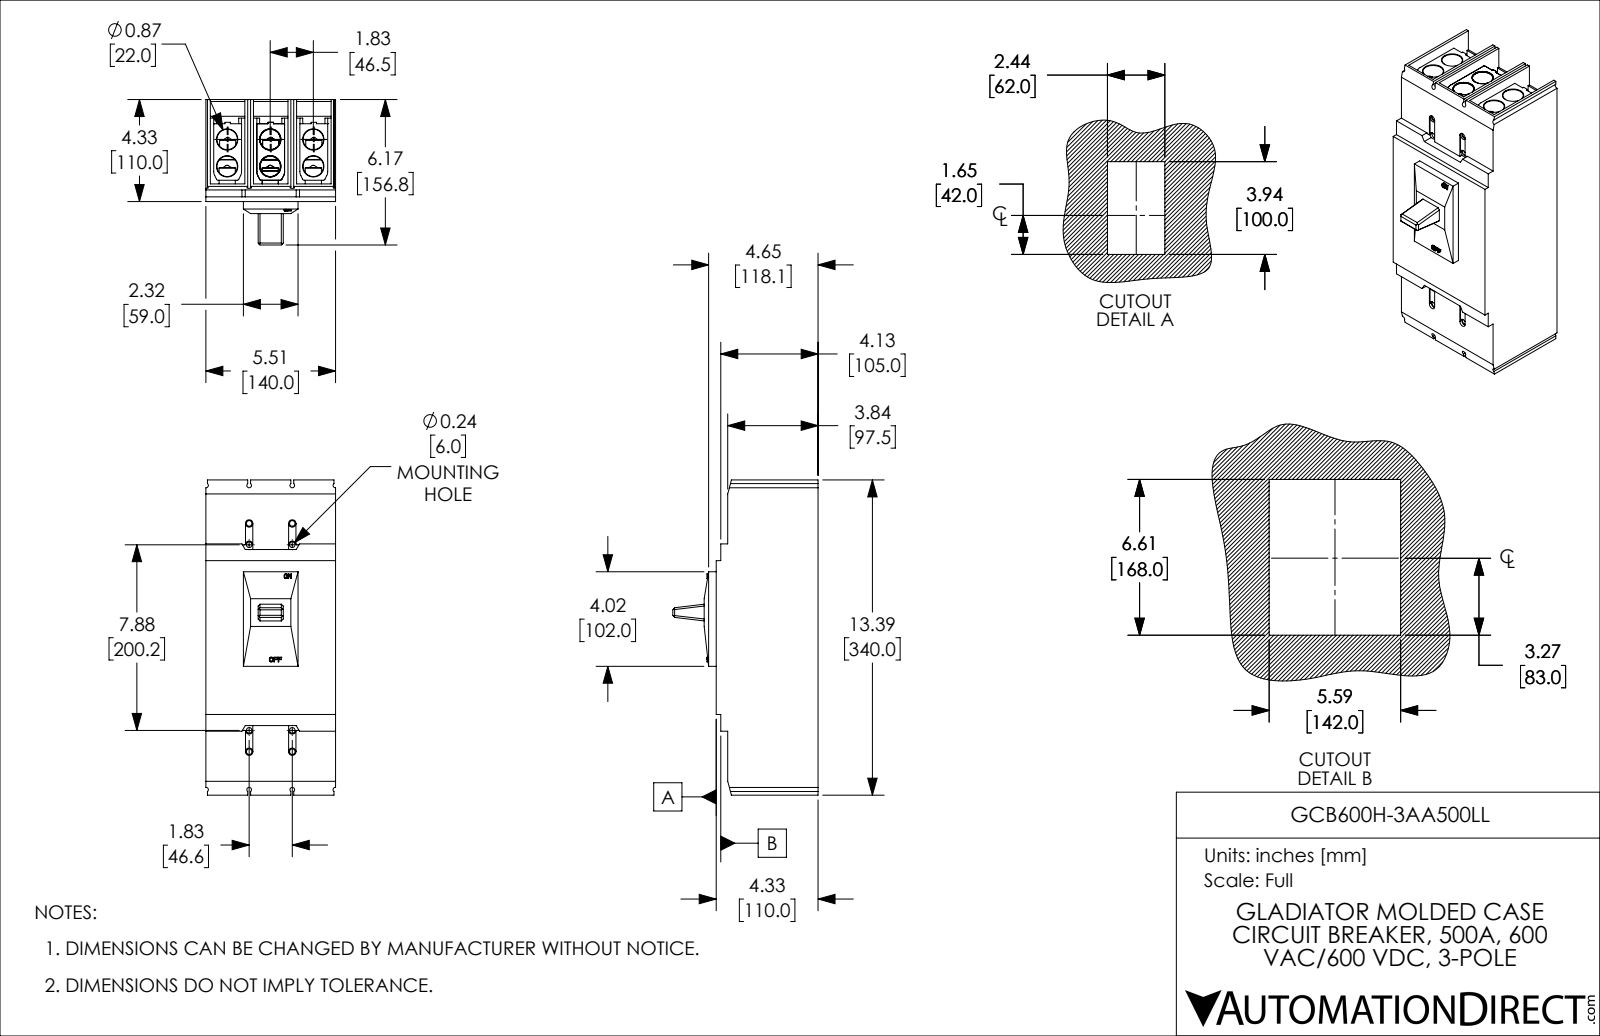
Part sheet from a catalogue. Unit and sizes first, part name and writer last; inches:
Units: inches
Overall size (bounding box): 13.386 × 6.173 × 5.512
Round holes (diameter × count): ⌀0.688 ×12, ⌀0.866 ×12, ⌀0.236 ×8, ⌀0.413 ×6, ⌀0.594 ×6, ⌀0.197 ×4, ⌀0.315 ×4
Round bosses / shafts (diameter × count): ⌀0.75 ×1
Partial cylindrical surfaces — rounded edges, fillets, slot ends (radius × count): R0.079 ×64, R0.394 ×12, R0.02 ×4, R0.098 ×4, R0.157 ×4
Main face-to-face distances: 1.833, 1.469, 5.512, 2.021, 0.189, 5.323, 3.491, 1.658, 3.854, 0.363
Hole centre spacings: 1.831, 2.157, 3.661, 0.041, 1.142, 1.143, 1.24, 1.832
Volume: 239.4 in³ · Surface area: 777.1 in²
Bodies: 24 solids, 1230 faces (691 planar, 266 cylindrical, 273 other)
Part name (STEP PRODUCT): GCB600H-3AA500LL
STEP written by: SolidWorks 2021 (CONFIG_CONTROL_DESIGN)
